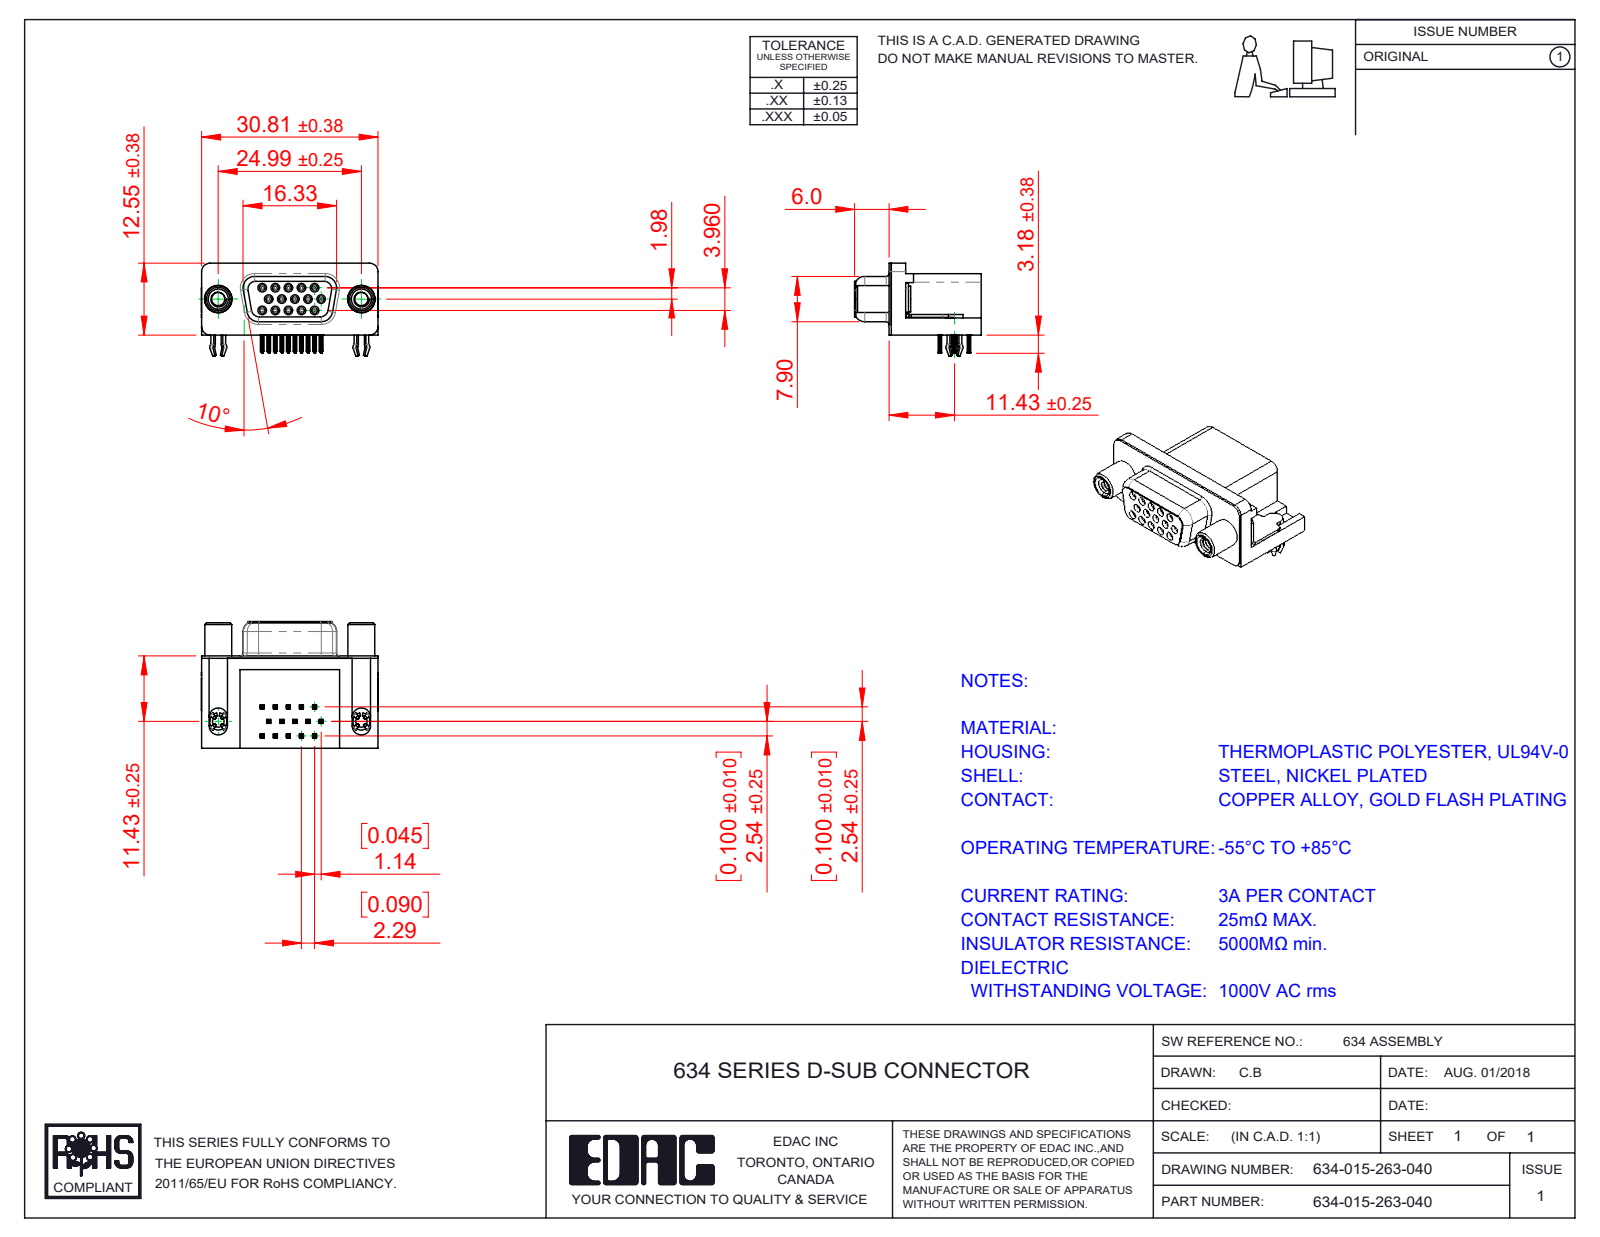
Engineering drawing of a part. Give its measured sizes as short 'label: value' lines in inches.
name: 634-015-263-040; Round Threaded Standoff; 4 Prong Board Lock; Contact Top (+4 more)
written by: SolidWorks 2016 (CONFIG_CONTROL_DESIGN)
unit: in
bodies: 21 solids, 2535 faces (1100 planar, 613 cylindrical, 822 other)
size: 1.216 × 0.87 × 0.64
volume: 0.284 in³; area: 10.5 in²
holes: 15× ⌀0.031, 15× ⌀0.035, 2× ⌀0.079, 2× ⌀0.091, 2× ⌀0.122, 2× ⌀0.157, 2× ⌀0.189, 2× ⌀0.197
bosses: 15× ⌀0.047, 2× ⌀0.193, 2× ⌀0.185, 2× ⌀0.177, 2× ⌀0.152, 2× ⌀0.118
rounds: 120× R0.004, 60× R0.006, 30× R0.014, 19× R0.039, 15× R0.013, 8× R0.053, 8× R0.063, 7× R0.059
face distances: 0.016, 0.407, 0.618, 0.634, 0.014, 0.098, 0.114, 0.024, 0.421, 0.264
hole spacings: 0.09, 0.09, 0.156, 0.18, 0.238, 0.156, 0.18, 0.27
